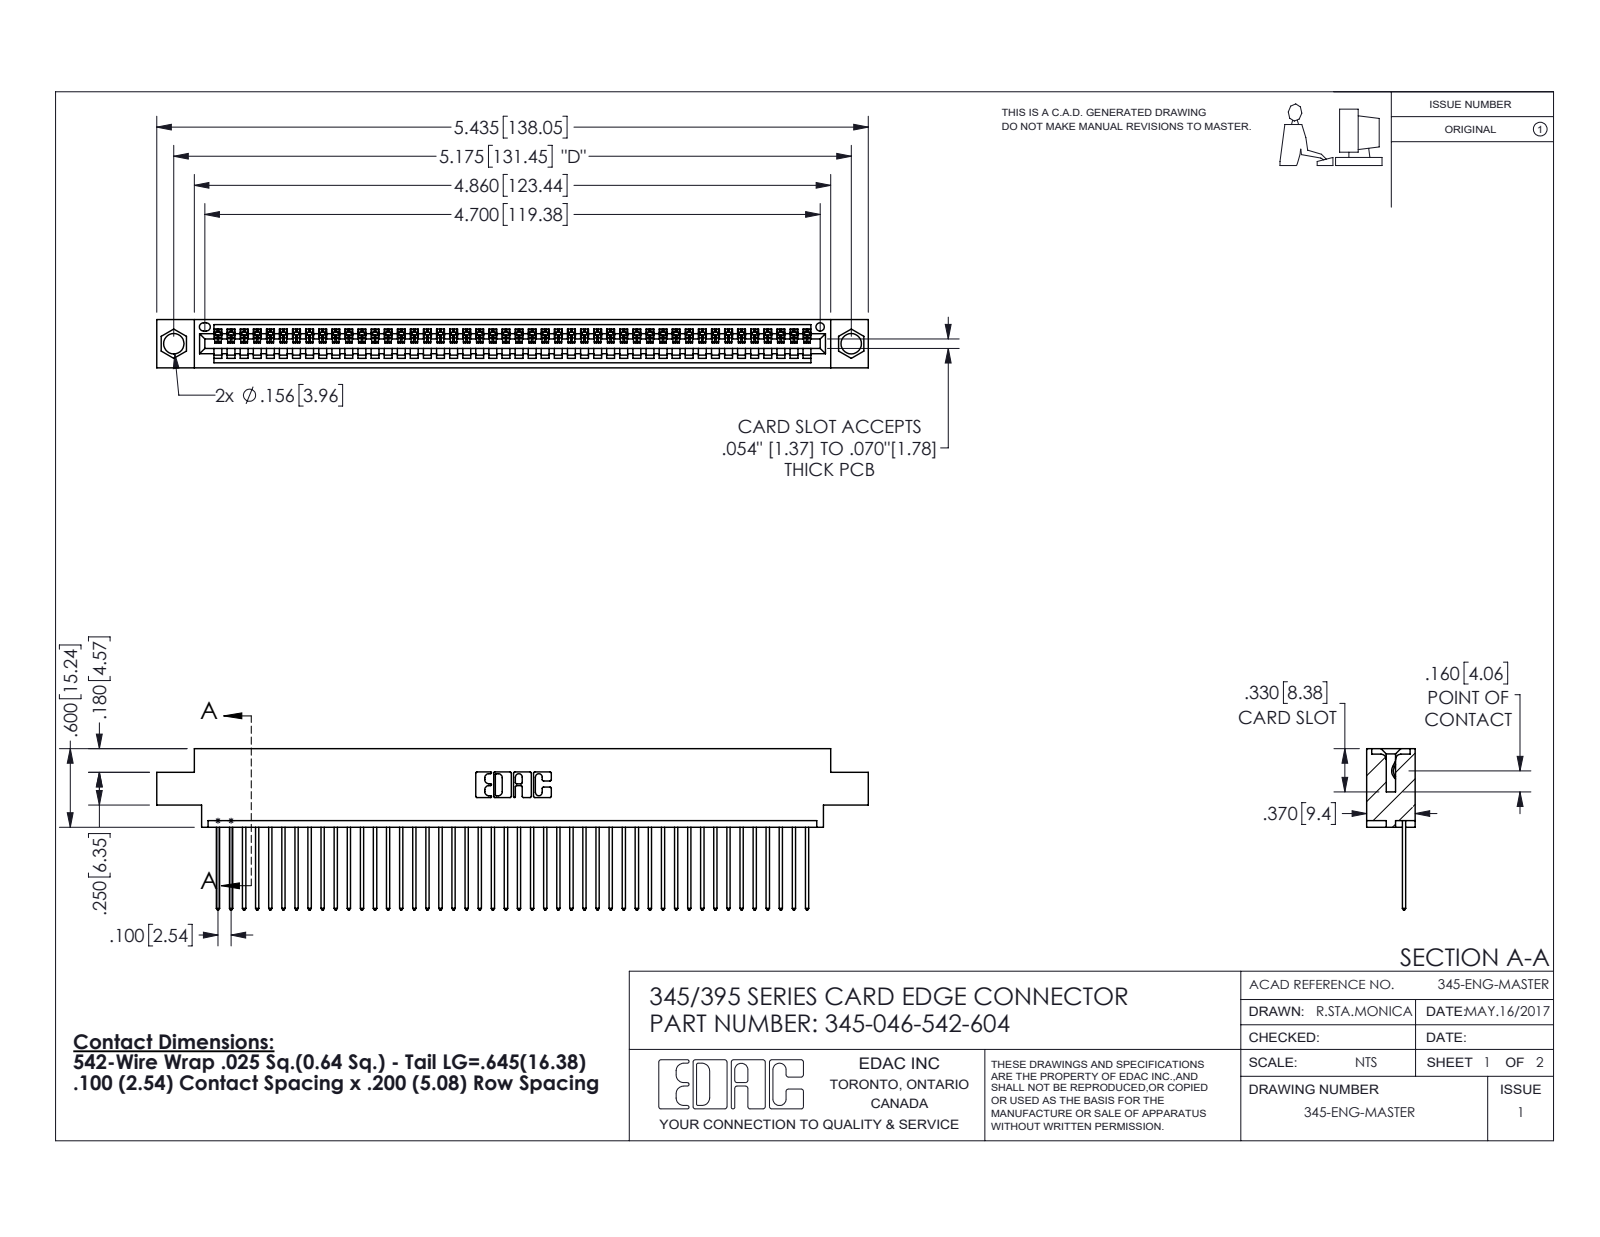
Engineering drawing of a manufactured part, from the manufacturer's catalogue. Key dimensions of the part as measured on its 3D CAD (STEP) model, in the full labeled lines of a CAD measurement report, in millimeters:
Part name (STEP PRODUCT): 345 Part_0.170 Offset - 0.156 Dia-TI; 345-292-001_345-293-142; 345-046-542-604
STEP written by: SolidWorks 2020 (CONFIG_CONTROL_DESIGN)
Units: millimetres
Bodies: 47 solids, 2812 faces (1938 planar, 874 cylindrical, 0 other)
Overall size (bounding box): 138 × 31.3 × 9.4
Volume: 13 000 mm³ · Surface area: 17 980 mm²
Round holes (diameter × count): ⌀4 ×2, ⌀1.6 ×1
Partial cylindrical surfaces — rounded edges, fillets, slot ends (radius × count): R0.2 ×92, R0.3 ×92, R0.3 ×22, R0.2 ×6, R0.8 ×6, R0.7 ×3, R0.8 ×2, R1 ×2
Main face-to-face distances: 1.8, 7.6, 9.4, 2.5, 6.9, 0.6, 5.1, 5.7, 4.4, 3.8
Hole centre spacings: 6.9, 125.5, 131.4
